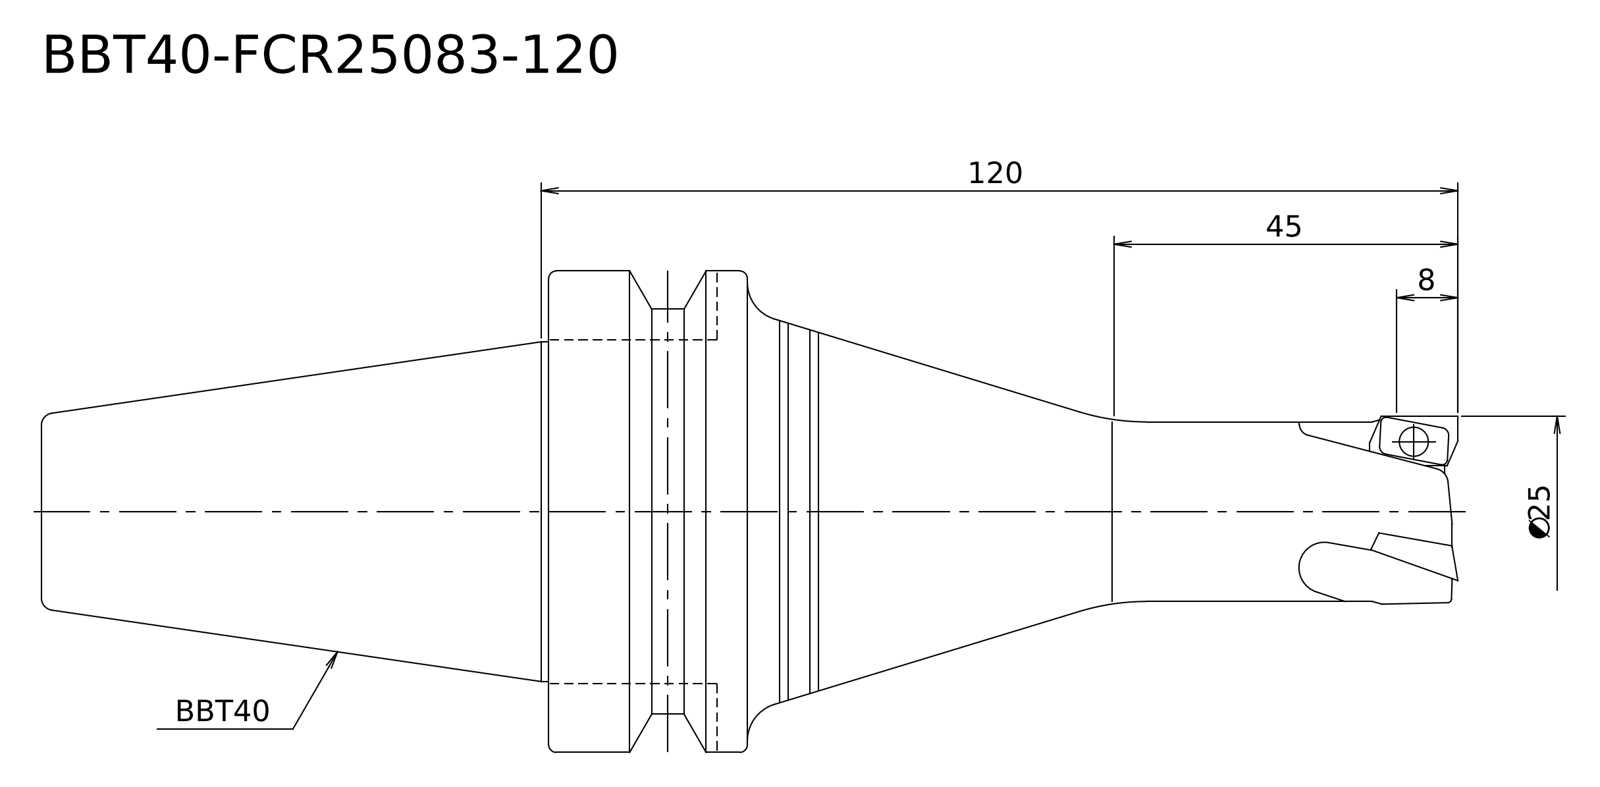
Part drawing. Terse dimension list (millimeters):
written by: Kubotek KeyCreator V8.5.1 (14335) (CONFIG_CONTROL_DESIGN)
unit: mm
bodies: 1 solid, 17 faces (4 planar, 6 cylindrical, 7 other)
size: 185.4 × 63 × 63
volume: 218 655 mm³; area: 26 018 mm²
bosses: 1× ⌀63, 1× ⌀53, 1× ⌀44.45, 1× ⌀25, 1× ⌀23.5
face distances: 66.4, 119, 185.4, 93, 26, 92.4
